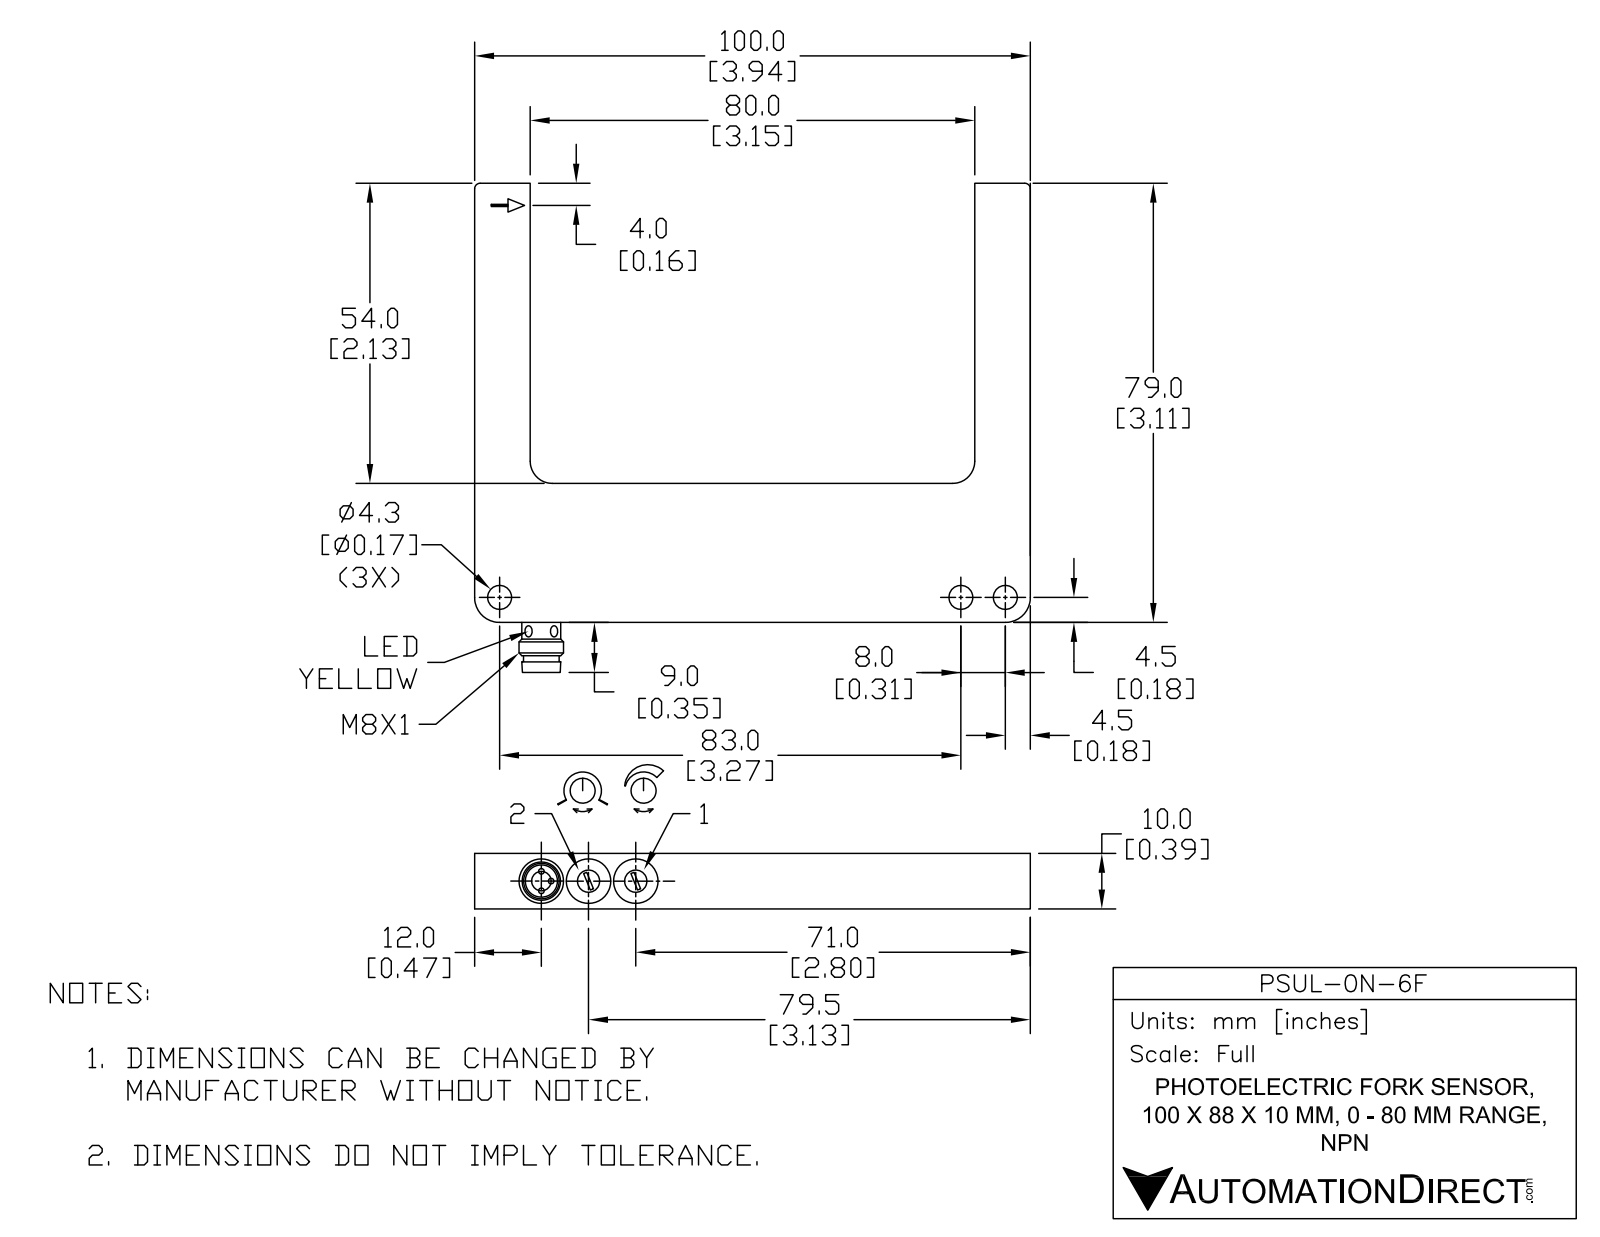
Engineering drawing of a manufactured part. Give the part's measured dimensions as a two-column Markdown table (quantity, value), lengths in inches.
| quantity | value |
| --- | --- |
| part name | PSUL-0N-6F |
| STEP written by | SolidWorks 2019 (AUTOMOTIVE_DESIGN) |
| units | inches |
| bodies | 1 solid, 95 faces (35 planar, 48 cylindrical, 12 other) |
| overall size | 3.937 × 3.465 × 0.394 |
| volume | 2.17 in³ |
| surface area | 19.25 in² |
| round holes (diameter × count) | 0.169 × 3, 0.079 × 2, 0.157 × 2, 0.315 × 2, 0.228 × 1 |
| round bosses / shafts (diameter × count) | 0.039 × 3, 0.315 × 1, 0.267 × 1 |
| partial cylindrical surfaces (radius × count) | 0.02 × 2, 0.039 × 2, 0.063 × 2, 0.157 × 2, 0.177 × 2 |
| main face-to-face distances | 0.394, 3.543, 3.937, 0.984, 3.15, 2.126, 3.11, 3.106, 0.98, 0.157 |
| hole center spacings | 0.335, 0.315, 0.669, 3.268, 3.583 |
